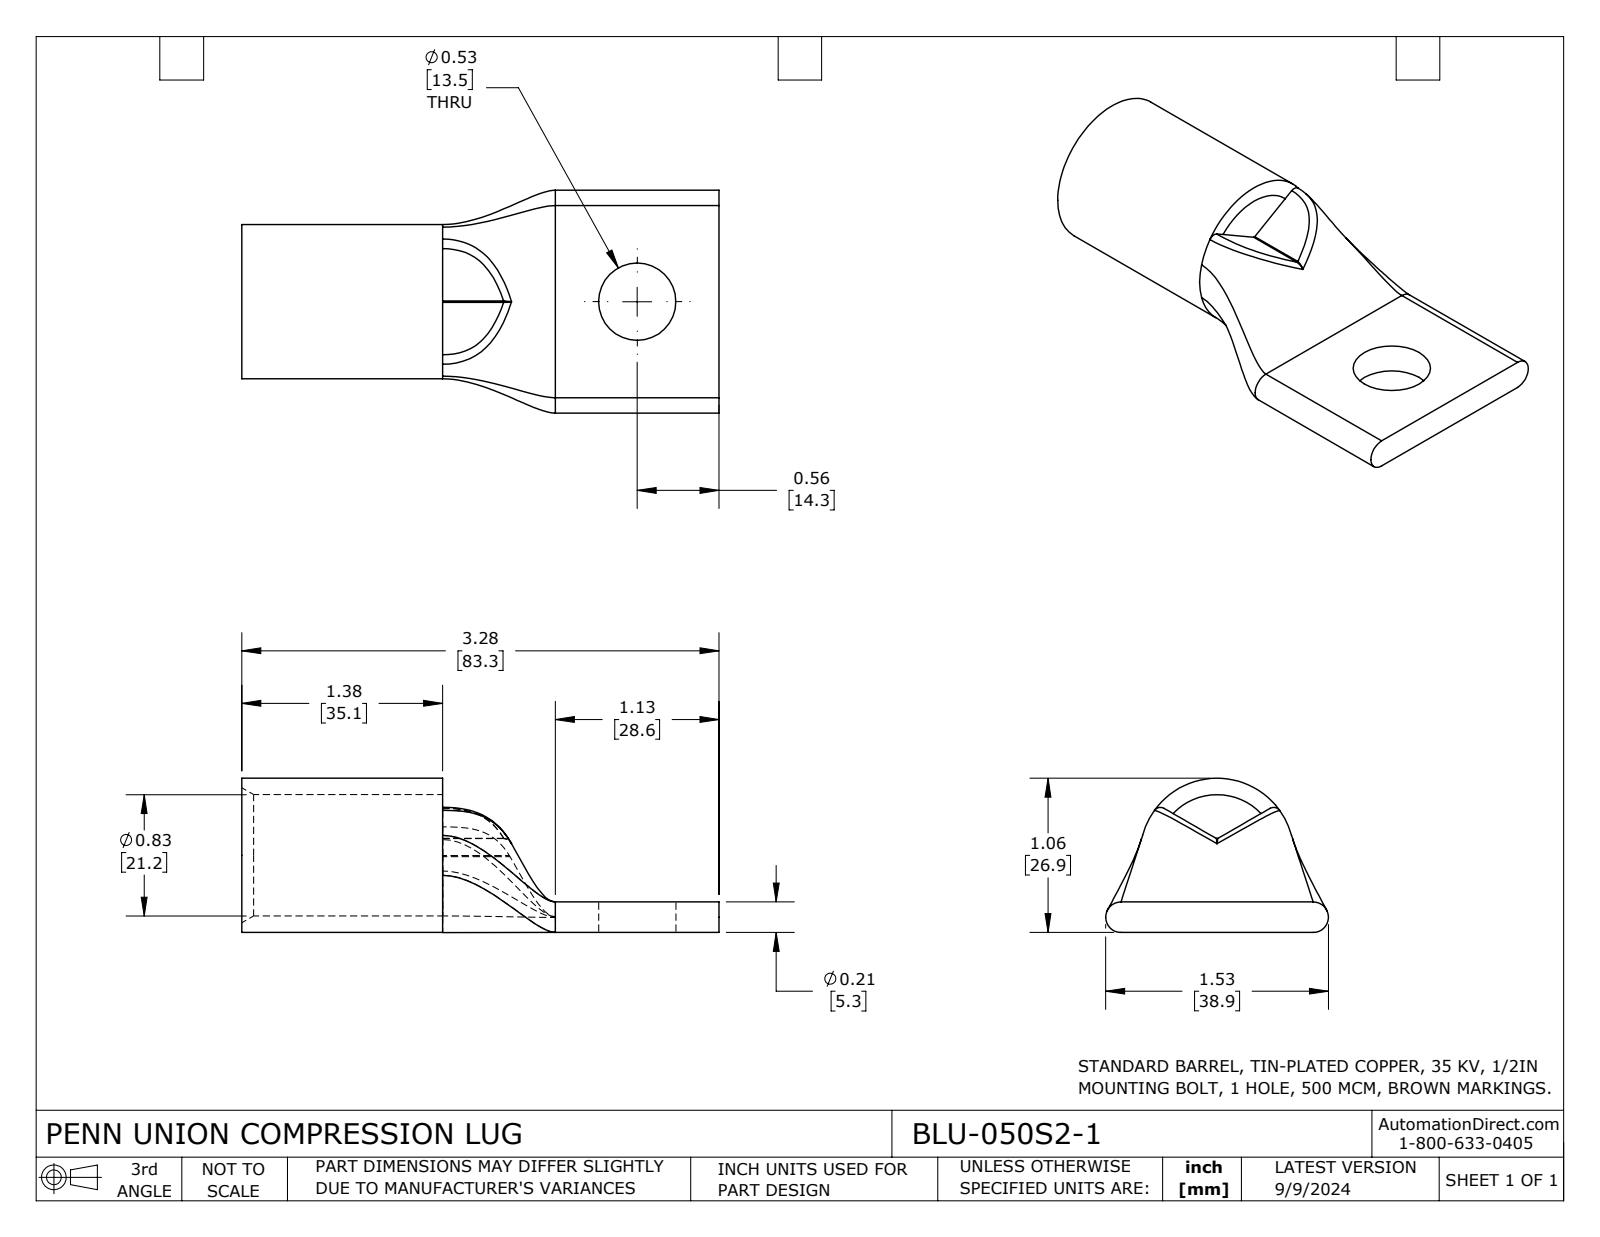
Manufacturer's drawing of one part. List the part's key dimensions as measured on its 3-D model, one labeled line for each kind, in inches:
Part name (STEP PRODUCT): BLU-050S2-1
STEP written by: SolidWorks 2023 (CONFIG_CONTROL_DESIGN)
Units: inches
Bodies: 1 solid, 35 faces (11 planar, 11 cylindrical, 13 other)
Overall size (bounding box): 3.28 × 1.531 × 1.06
Volume: 0.998 in³ · Surface area: 17.7 in²
Round holes (diameter × count): ⌀0.531 ×1, ⌀0.834 ×1
Round bosses / shafts (diameter × count): ⌀1.06 ×1
Partial cylindrical surfaces — rounded edges, fillets, slot ends (radius × count): R0.105 ×2, R0.01 ×1, R0.05 ×1
Main face-to-face distances: 0.21, 0.113, 3.28, 1.38, 1.9, 2.155, 0.775, 1.125
